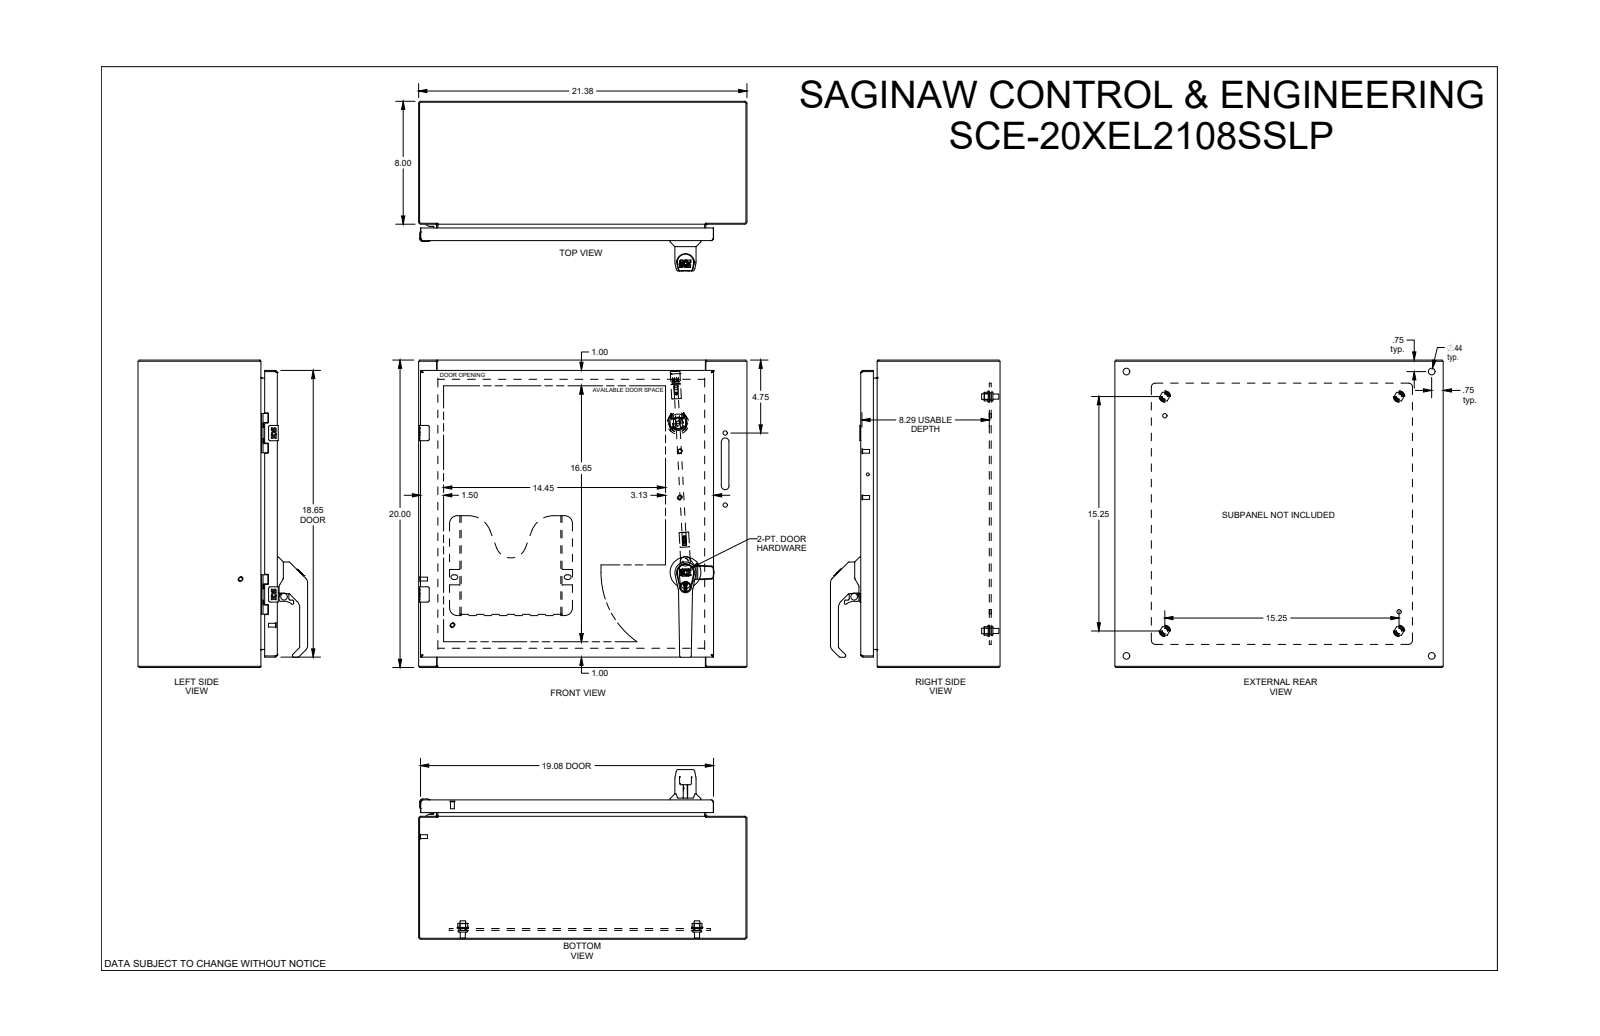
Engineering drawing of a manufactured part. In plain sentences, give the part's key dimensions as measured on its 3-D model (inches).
The part is named "SCE-20XEL2108SSLP". Its 3-D file was written by "SolidWorks 2021 (AUTOMOTIVE_DESIGN)". It is 67 solids with 4458 faces: 1625 planar, 1197 cylindrical and 1636 other. Overall it measures 21.375 by 20 by 11.041 inches. Its volume is 182.1 cubic inches and its surface area 4 352 square inches. Round holes: 5 of diameter 0.266, 4 of diameter 0.172, 4 of diameter 0.205, 4 of diameter 0.244, 4 of diameter 0.281, 4 of diameter 0.367, 4 of diameter 0.375, 4 of diameter 0.437, 4 of diameter 0.5, 3 of diameter 0.25, 2 of diameter 0.04, 2 of diameter 0.138. Round bosses or shafts: 7 of diameter 0.248, 6 of diameter 0.17, 4 of diameter 0.366, 4 of diameter 0.332, 4 of diameter 0.25, 4 of diameter 0.24, 3 of diameter 0.563, 3 of diameter 0.196. Partial cylindrical surfaces (rounded edges, fillets, slot ends): 67 of radius 0.03, 50 of radius 0.015, 43 of radius 0.02, 34 of radius 0.02, 32 of radius 0.01, 28 of radius 0.039, 26 of radius 0.005, 25 of radius 0.04. The main face-to-face distances are 0.075, 0.075, 8.998, 0.06, 9.073, 9.013, 8.938, 21.3, 0.125, 0.5. The hole center spacings are 0.985, 15.25, 4.493, 10.5, 14.993, 0.02, 0.472, 0.493.
